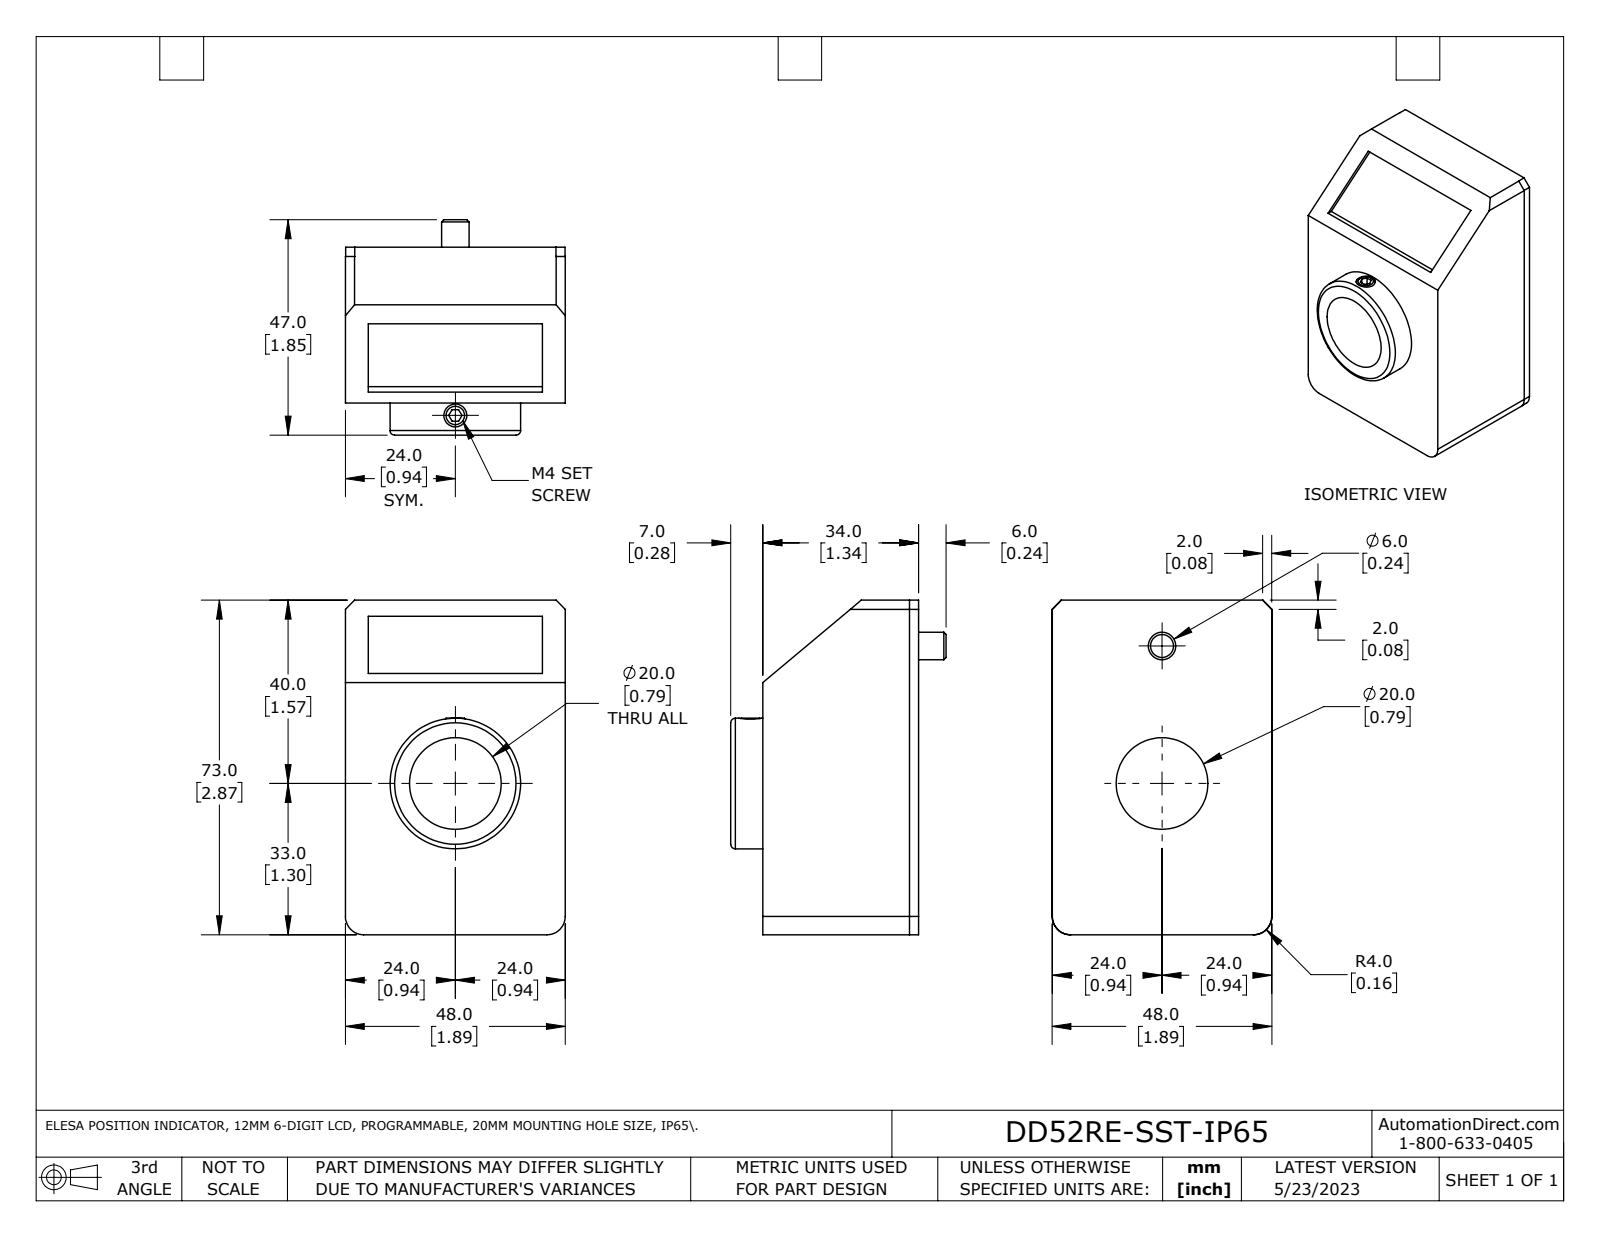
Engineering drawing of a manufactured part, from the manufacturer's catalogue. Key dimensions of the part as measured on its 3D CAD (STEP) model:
Part name (STEP PRODUCT): DD52RE-SST-IP65
STEP written by: SolidWorks 2021 (AUTOMOTIVE_DESIGN)
Units: inches
Bodies: 1 solid, 53 faces (38 planar, 11 cylindrical, 4 other)
Overall size (bounding box): 2.874 × 1.89 × 1.85
Volume: 6.076 in³ · Surface area: 26.77 in²
Round holes (diameter × count): ⌀0.197 ×1, ⌀0.787 ×1, ⌀1.122 ×1
Round bosses / shafts (diameter × count): ⌀0.965 ×1, ⌀0.236 ×1
Partial cylindrical surfaces — rounded edges, fillets, slot ends (radius × count): R0.157 ×4
Main face-to-face distances: 1.339, 1.89, 0.03, 2.874, 1.888, 0.197, 1.142, 0.177, 0.02, 1.161
